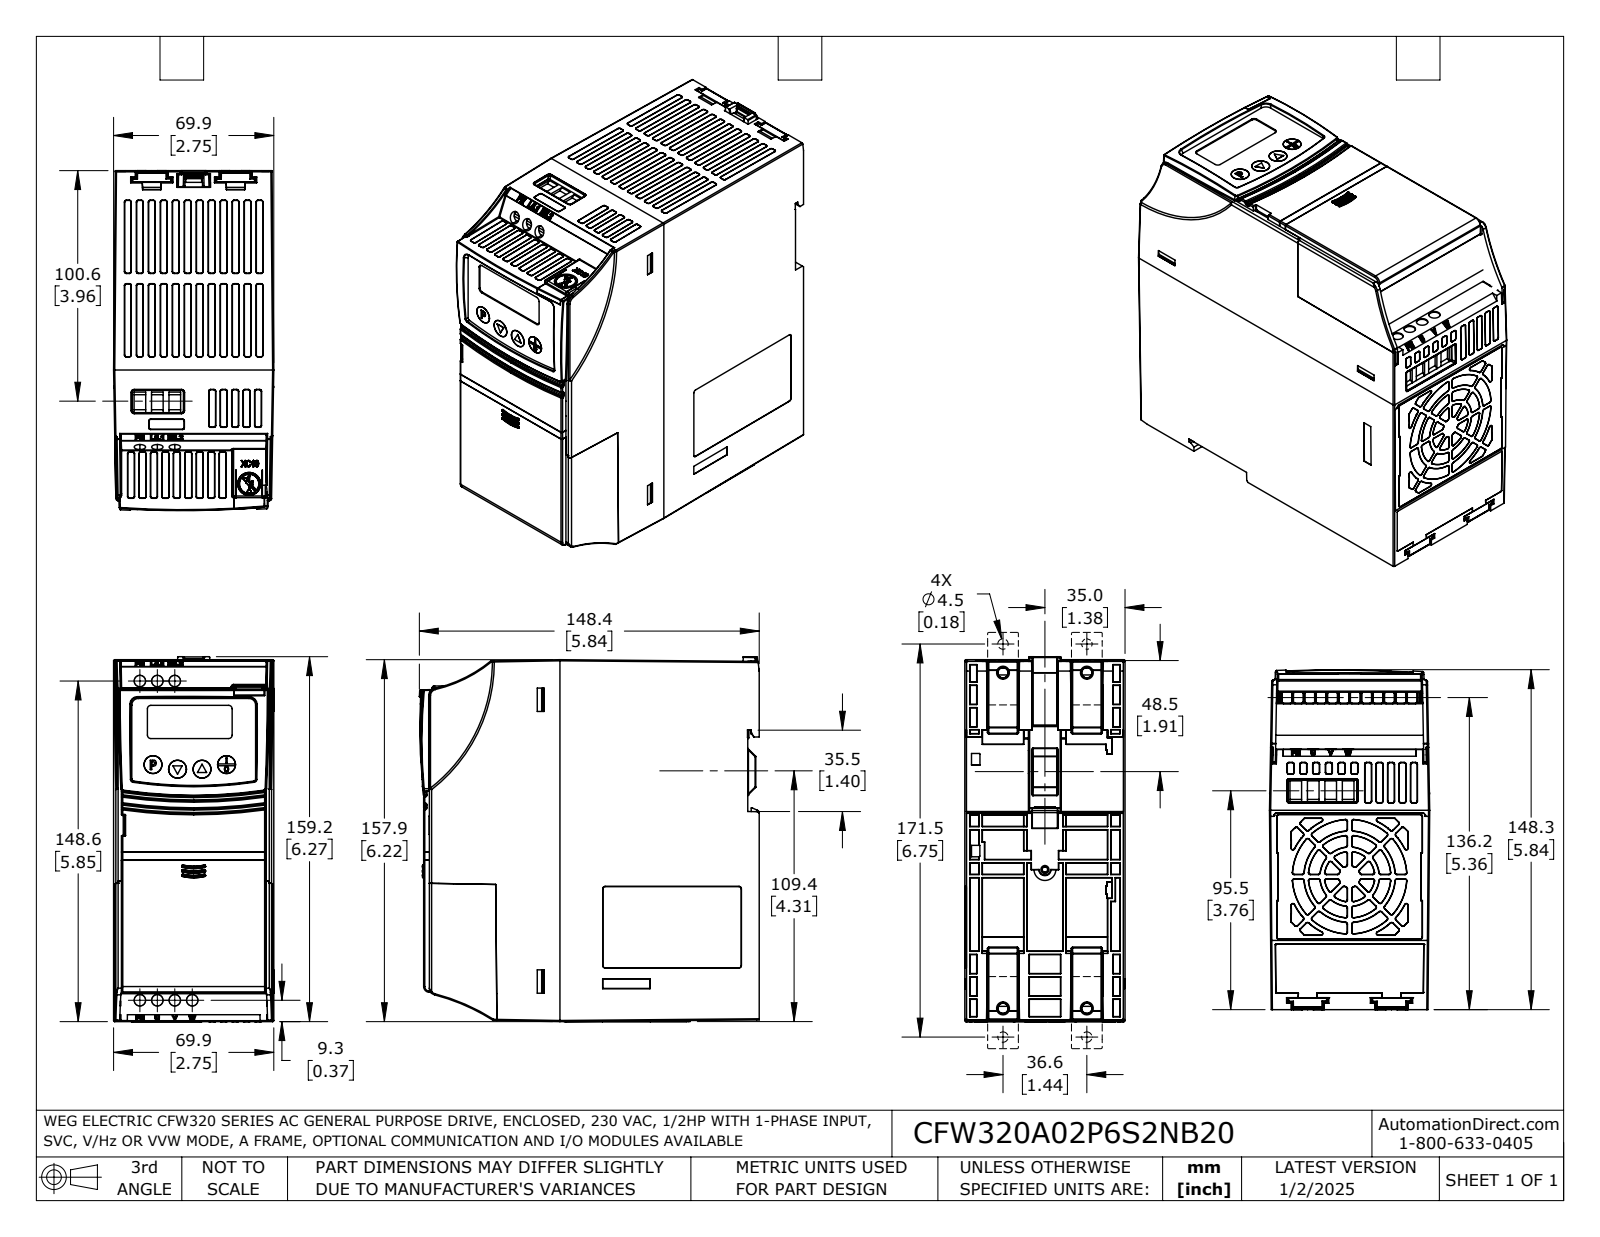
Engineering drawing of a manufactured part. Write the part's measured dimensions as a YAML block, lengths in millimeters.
part_name: "CFW320A02P6S2NB20"
step_written_by: "SolidWorks 2021 (AUTOMOTIVE_DESIGN)"
units: millimeters
bodies: {solids: 6, faces: 3715, planar: 1587, cylindrical: 853, other: 1275}
overall_size: [159.2, 148.4, 70]
volume: 249700
surface_area: 199400
round_holes:
  - {diameter: 5, count: 3}
partial_cylinders:
  - {radius: 0.3, count: 327}
  - {radius: 0.5, count: 150}
  - {radius: 1, count: 13}
  - {radius: 0.8, count: 5}
  - {radius: 3, count: 3}
  - {radius: 0.3, count: 2}
  - {radius: 2.5, count: 1}
  - {radius: 3.2, count: 1}
face_to_face_distances: [1.8, 1.4, 0.5, 1.3, 152.4, 135.4, 134, 141.5, 140.1, 6.1]
hole_center_spacings: [7.6, 15.2]
